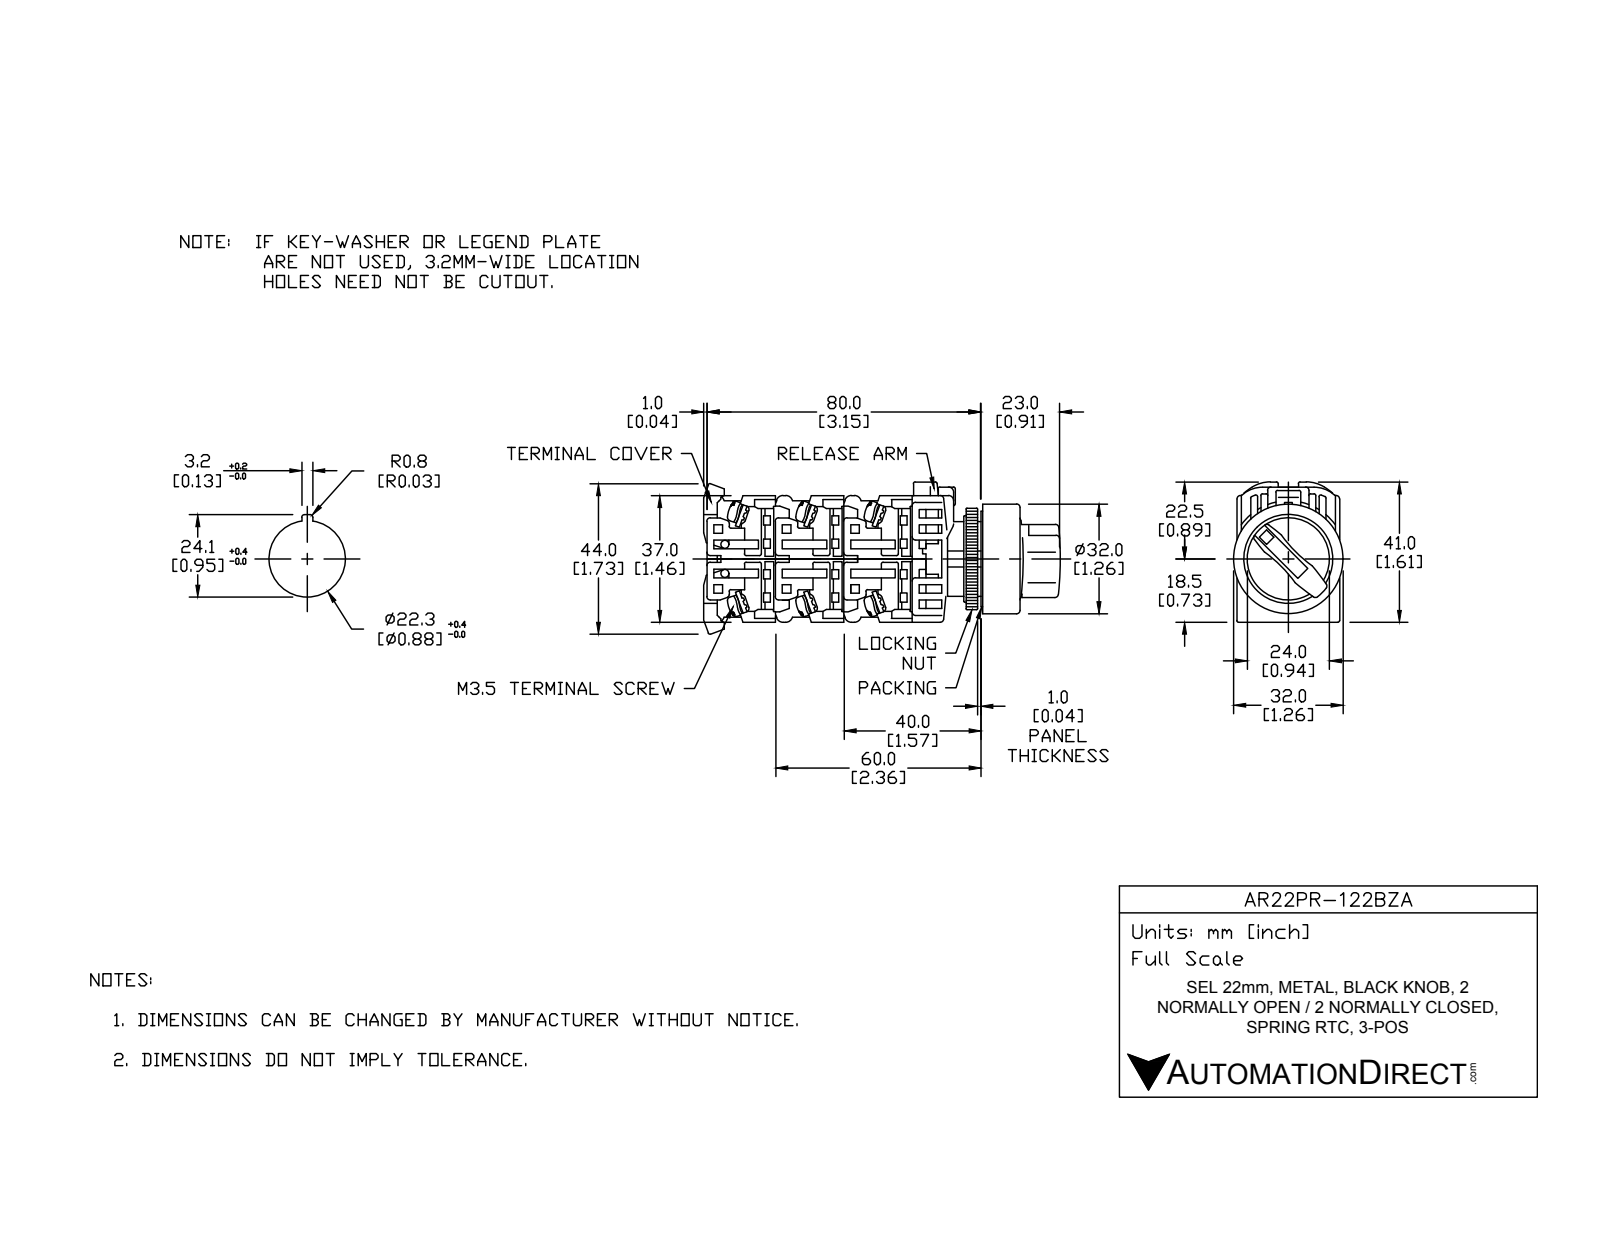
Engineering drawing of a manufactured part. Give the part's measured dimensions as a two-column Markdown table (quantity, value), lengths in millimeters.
| quantity | value |
| --- | --- |
| part name | AR22PR-122BZA |
| STEP written by | SolidWorks 2017 (AUTOMOTIVE_DESIGN) |
| units | millimeters |
| bodies | 18 solids, 463 faces (317 planar, 118 cylindrical, 28 other) |
| overall size | 64 × 43.81 × 32 |
| volume | 38 439 mm³ |
| surface area | 24 800 mm² |
| round holes (diameter × count) | 21.8 × 1, 22 × 1, 25 × 1, 31 × 1 |
| round bosses / shafts (diameter × count) | 5 × 4, 32 × 1, 30.5 × 1, 29.8 × 1, 24 × 1, 21.75 × 1, 17 × 1 |
| partial cylindrical surfaces (radius × count) | 0.5 × 39, 1.75 × 8, 1 × 6, 5 × 4, 4 × 2, 12 × 1, 16.59 × 1, 17.59 × 1 |
| main face-to-face distances | 1, 18, 3, 28.5, 48.5, 20, 29, 0.5, 21, 10 |
